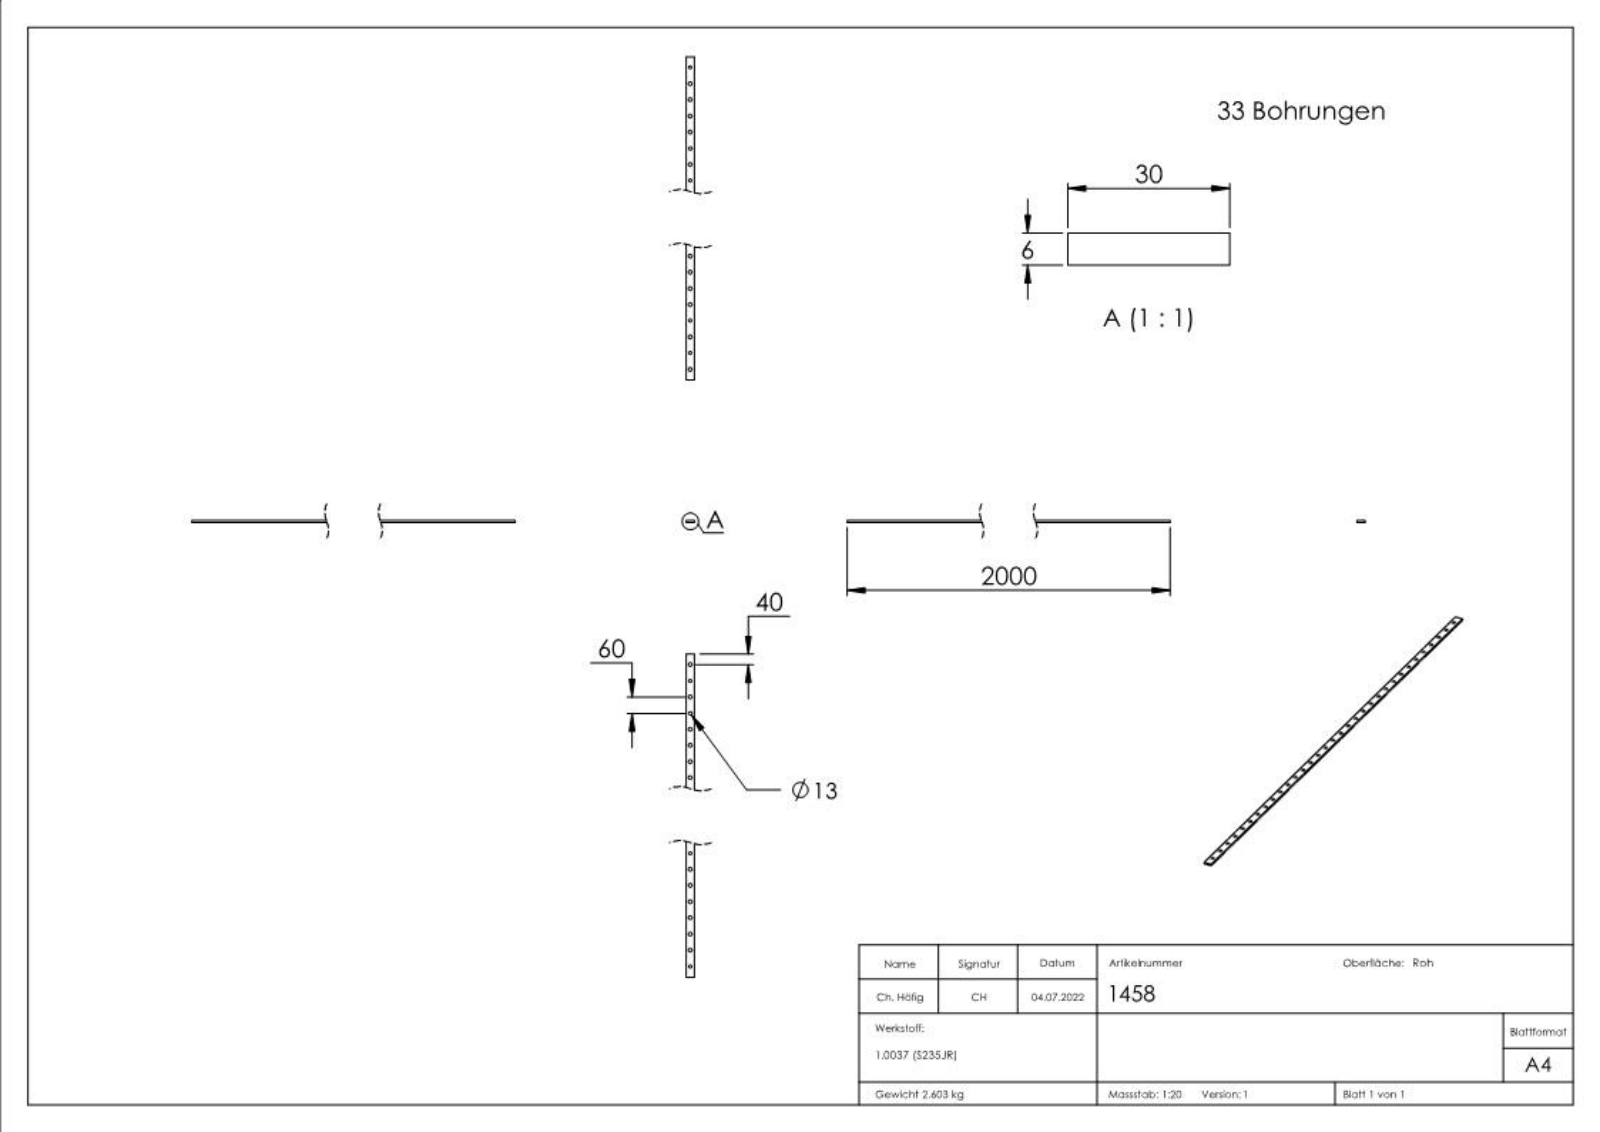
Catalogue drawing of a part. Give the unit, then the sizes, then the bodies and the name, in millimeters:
Units: millimetres
Overall size (bounding box): 2000 × 30 × 6
Round holes (diameter × count): ⌀13 ×33
Main face-to-face distances: 6, 30, 2000, 5.9, 15, 2.7, 3.66, 4.6, 3.54, 0.68
Hole centre spacings: 60, 120, 180, 240, 300, 360, 420, 480
Volume: 333 718 mm³ · Surface area: 143 696 mm²
Bodies: 1 solid, 252 faces (126 planar, 33 cylindrical, 93 other)
Part name (STEP PRODUCT): 1458
STEP written by: SolidWorks 2018 (CONFIG_CONTROL_DESIGN)
